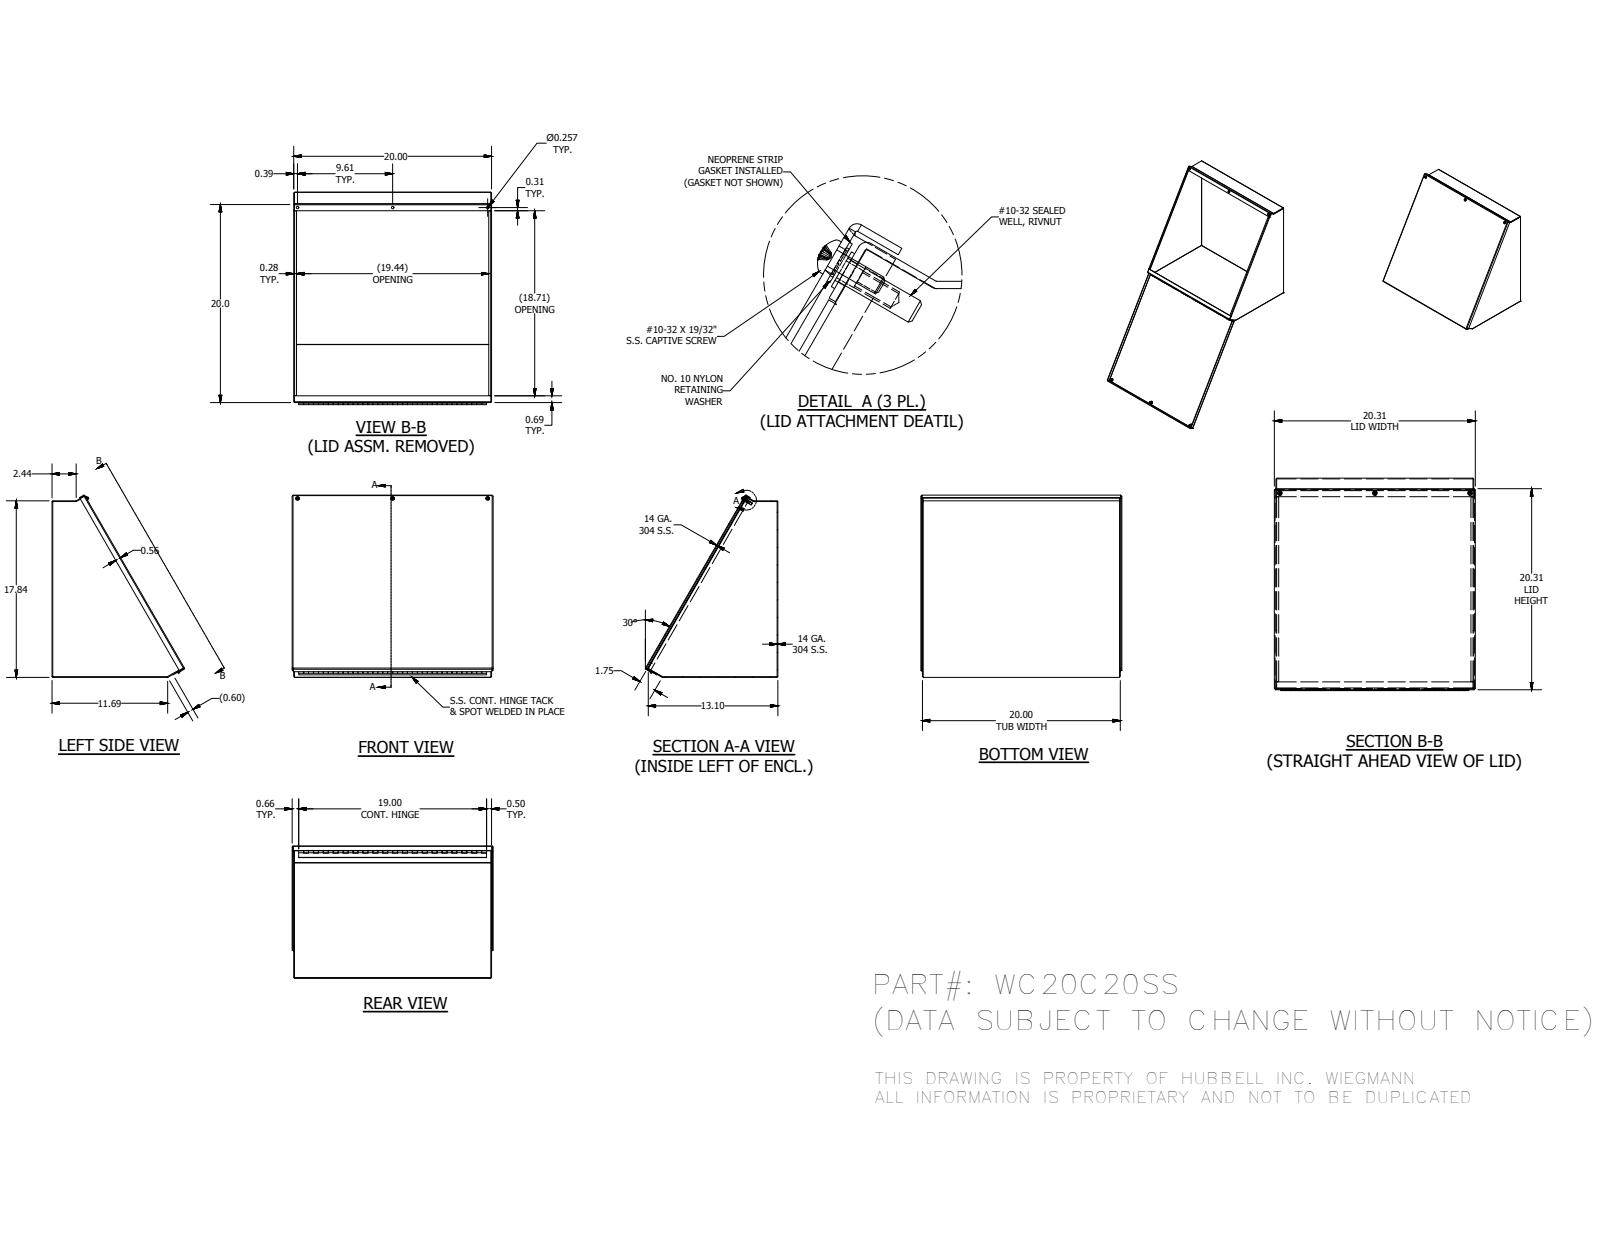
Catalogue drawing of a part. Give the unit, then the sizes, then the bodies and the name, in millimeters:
Units: millimetres
Overall size (bounding box): 515.94 × 467.99 × 340.03
Round holes (diameter × count): ⌀3.96 ×3, ⌀4.98 ×3, ⌀6.53 ×3, ⌀7.06 ×3, ⌀7.14 ×3, ⌀2.96 ×1
Round bosses / shafts (diameter × count): ⌀11.51 ×3, ⌀10.31 ×3, ⌀9.47 ×3, ⌀6.3 ×3, ⌀4.83 ×3, ⌀5.08 ×1, ⌀2.54 ×1
Partial cylindrical surfaces — rounded edges, fillets, slot ends (radius × count): R0.4 ×12, R2.28 ×12, R2.27 ×3
Main face-to-face distances: 1.88, 506.12, 504.24, 508, 451.35, 449.47, 453.23, 2.94, 3.97, 510.09
Hole centre spacings: 244.17, 488.34, 1.31
Volume: 1 797 000 mm³ · Surface area: 1 948 000 mm²
Bodies: 16 solids, 557 faces (340 planar, 143 cylindrical, 74 other)
Part name (STEP PRODUCT): WC20C20SSBTB; WC20C20SSLID; WC20CSSLS; WC20CSSRS (+8 more)
STEP written by: Autodesk Inventor 2014 (AUTOMOTIVE_DESIGN)
